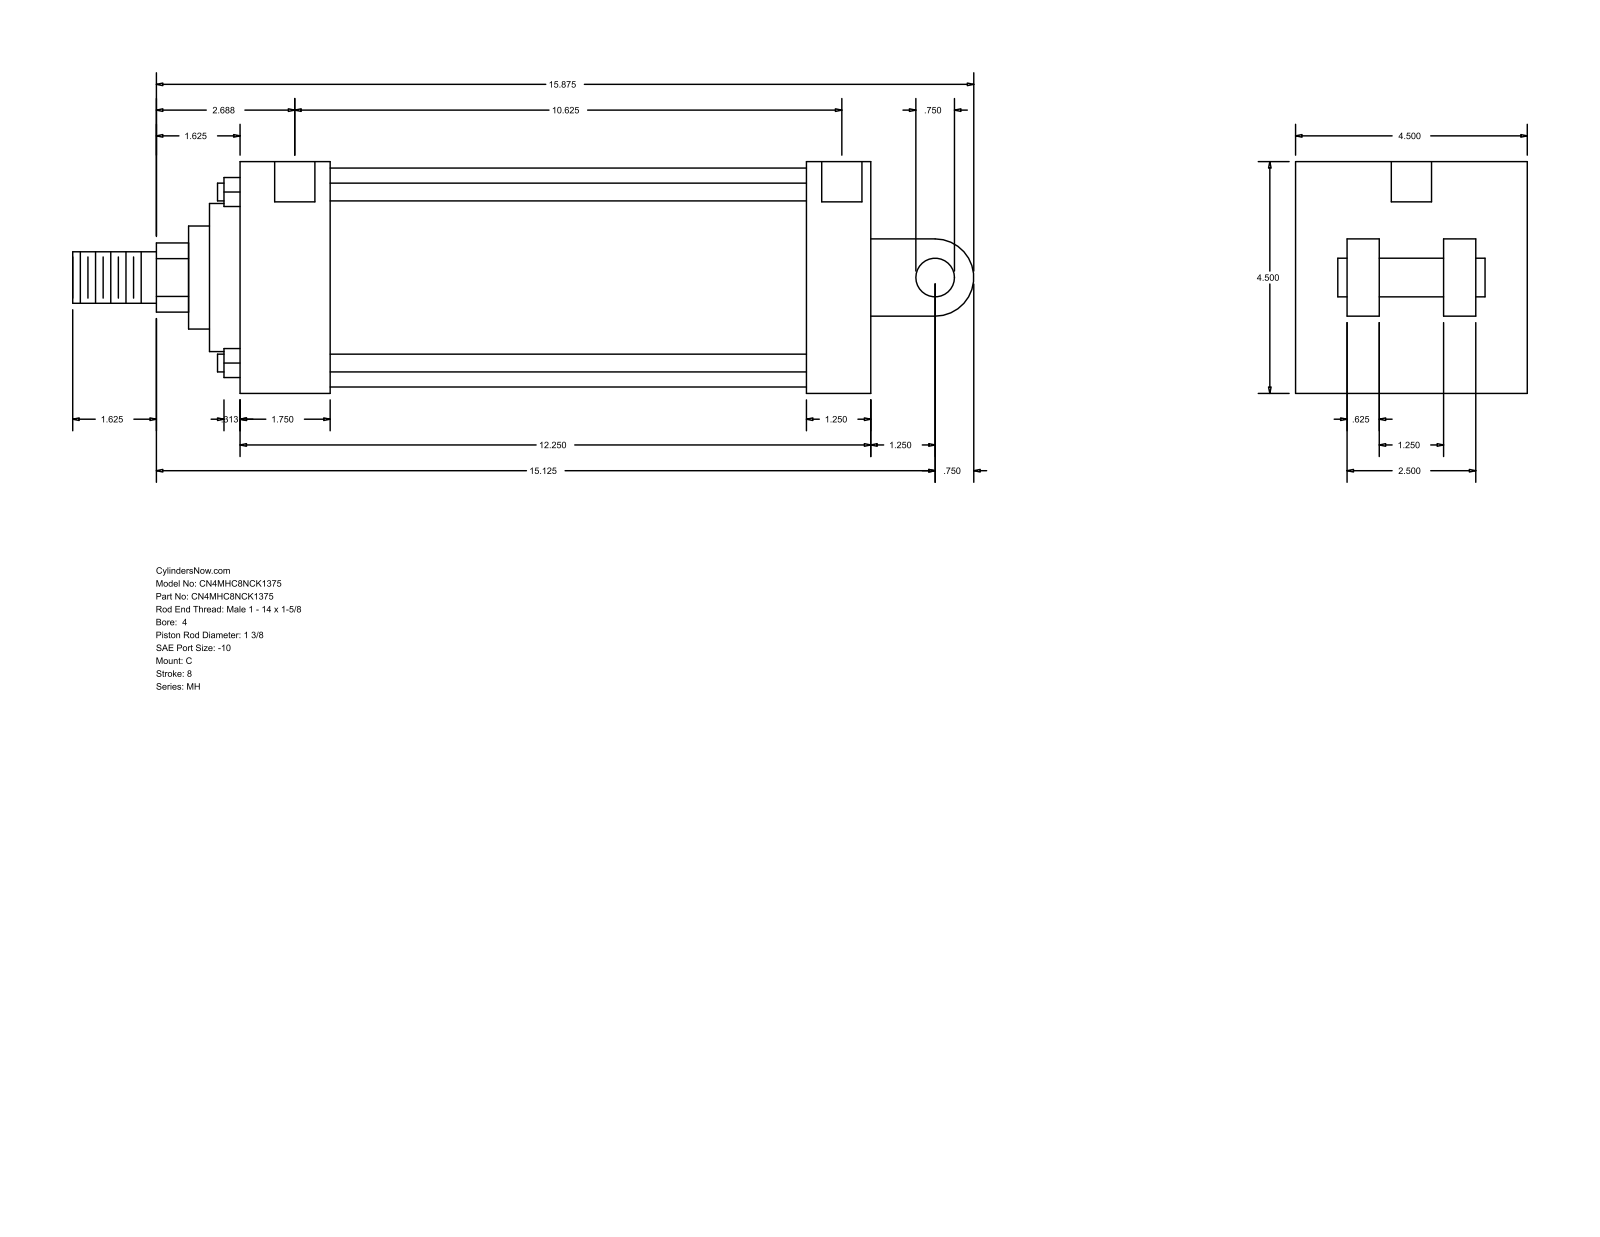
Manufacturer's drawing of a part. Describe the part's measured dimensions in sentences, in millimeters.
The part is named "MH_C__0400_1.375". Its 3-D file was written by "GSSL Pune (CONFIG_CONTROL_DESIGN)". It is 0 solids with 101 faces: 71 planar, 30 cylindrical and 0 other. Overall it measures 444.5 by 114.3 by 114.3 millimeters. Round holes: 4 of diameter 8.73, 2 of diameter 19.84. Round bosses or shafts: 4 of diameter 8.76, 1 of diameter 107.95, 1 of diameter 73.03, 1 of diameter 50.8, 1 of diameter 34.92, 1 of diameter 25.4, 1 of diameter 19.05. Partial cylindrical surfaces (rounded edges, fillets, slot ends): 1 of radius 17.06, 1 of radius 19.05. The main face-to-face distances are 114.3, 311.16, 44.45, 279.41, 234.96, 266.71, 31.75, 41.27, 73.03, 38.1. The hole center spacings are 1.59, 271.47, 273.06, 269.88.
